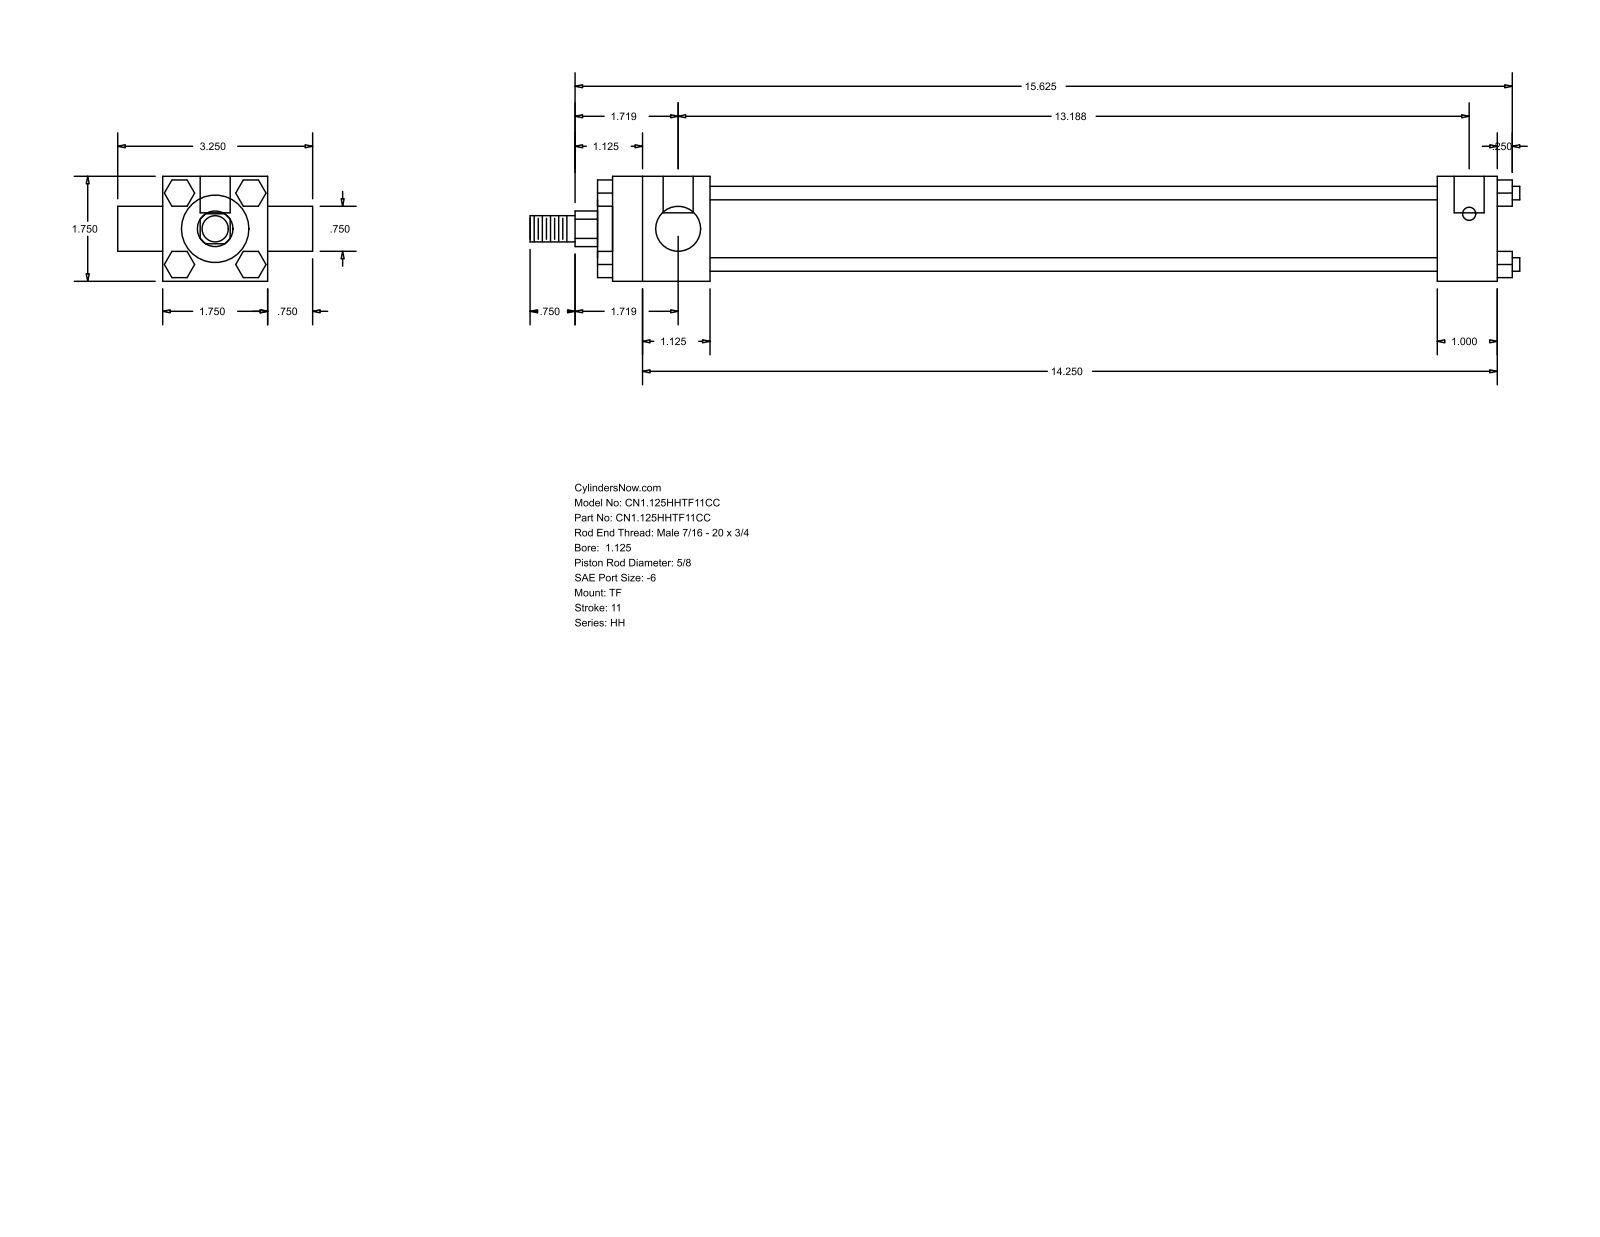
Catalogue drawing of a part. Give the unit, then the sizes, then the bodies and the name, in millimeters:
Units: millimetres
Overall size (bounding box): 419.1 × 82.55 × 44.45
Round holes (diameter × count): ⌀5.56 ×3, ⌀12.7 ×2
Round bosses / shafts (diameter × count): ⌀5.71 ×4, ⌀34.92 ×1, ⌀28.57 ×1, ⌀19.05 ×1, ⌀15.88 ×1, ⌀11.11 ×1
Partial cylindrical surfaces — rounded edges, fillets, slot ends (radius × count): R7.54 ×1
Main face-to-face distances: 44.46, 11.11, 25.4, 307.97, 333.37, 41.27, 349.24, 374.64, 47.62, 6.35
Hole centre spacings: 3.17, 331.79, 334.96
Bodies: 0 solids, 120 faces (92 planar, 28 cylindrical, 0 other)
Part name (STEP PRODUCT): HH_TF__0112_0.625
STEP written by: GSSL Pune (CONFIG_CONTROL_DESIGN)
